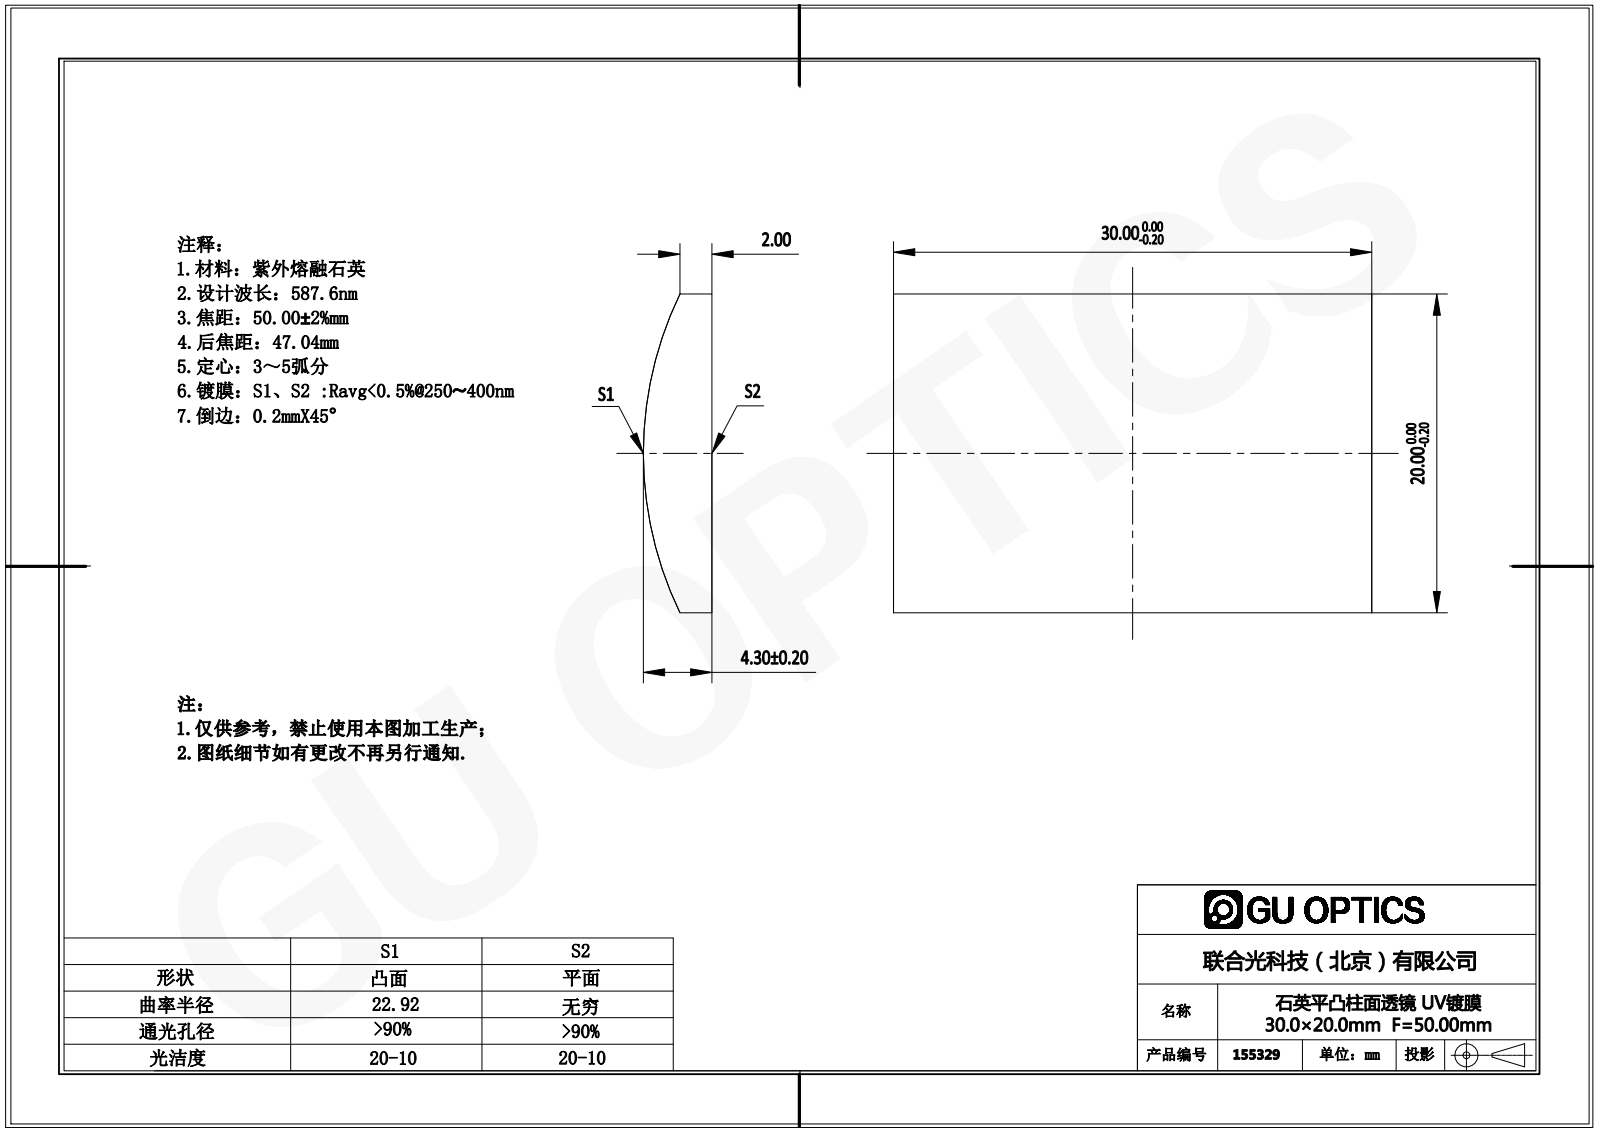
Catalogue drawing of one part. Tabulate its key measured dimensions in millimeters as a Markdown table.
| quantity | value |
| --- | --- |
| part name | 155295 |
| STEP written by | SolidWorks 2016 (AUTOMOTIVE_DESIGN) |
| units | millimeters |
| bodies | 1 solid, 6 faces (5 planar, 1 cylindrical, 0 other) |
| overall size | 30 × 20 × 4.3 |
| volume | 2 130 mm³ |
| surface area | 1 483 mm² |
| partial cylindrical surfaces (radius × count) | 22.92 × 1 |
| main face-to-face distances | 30, 20 |
